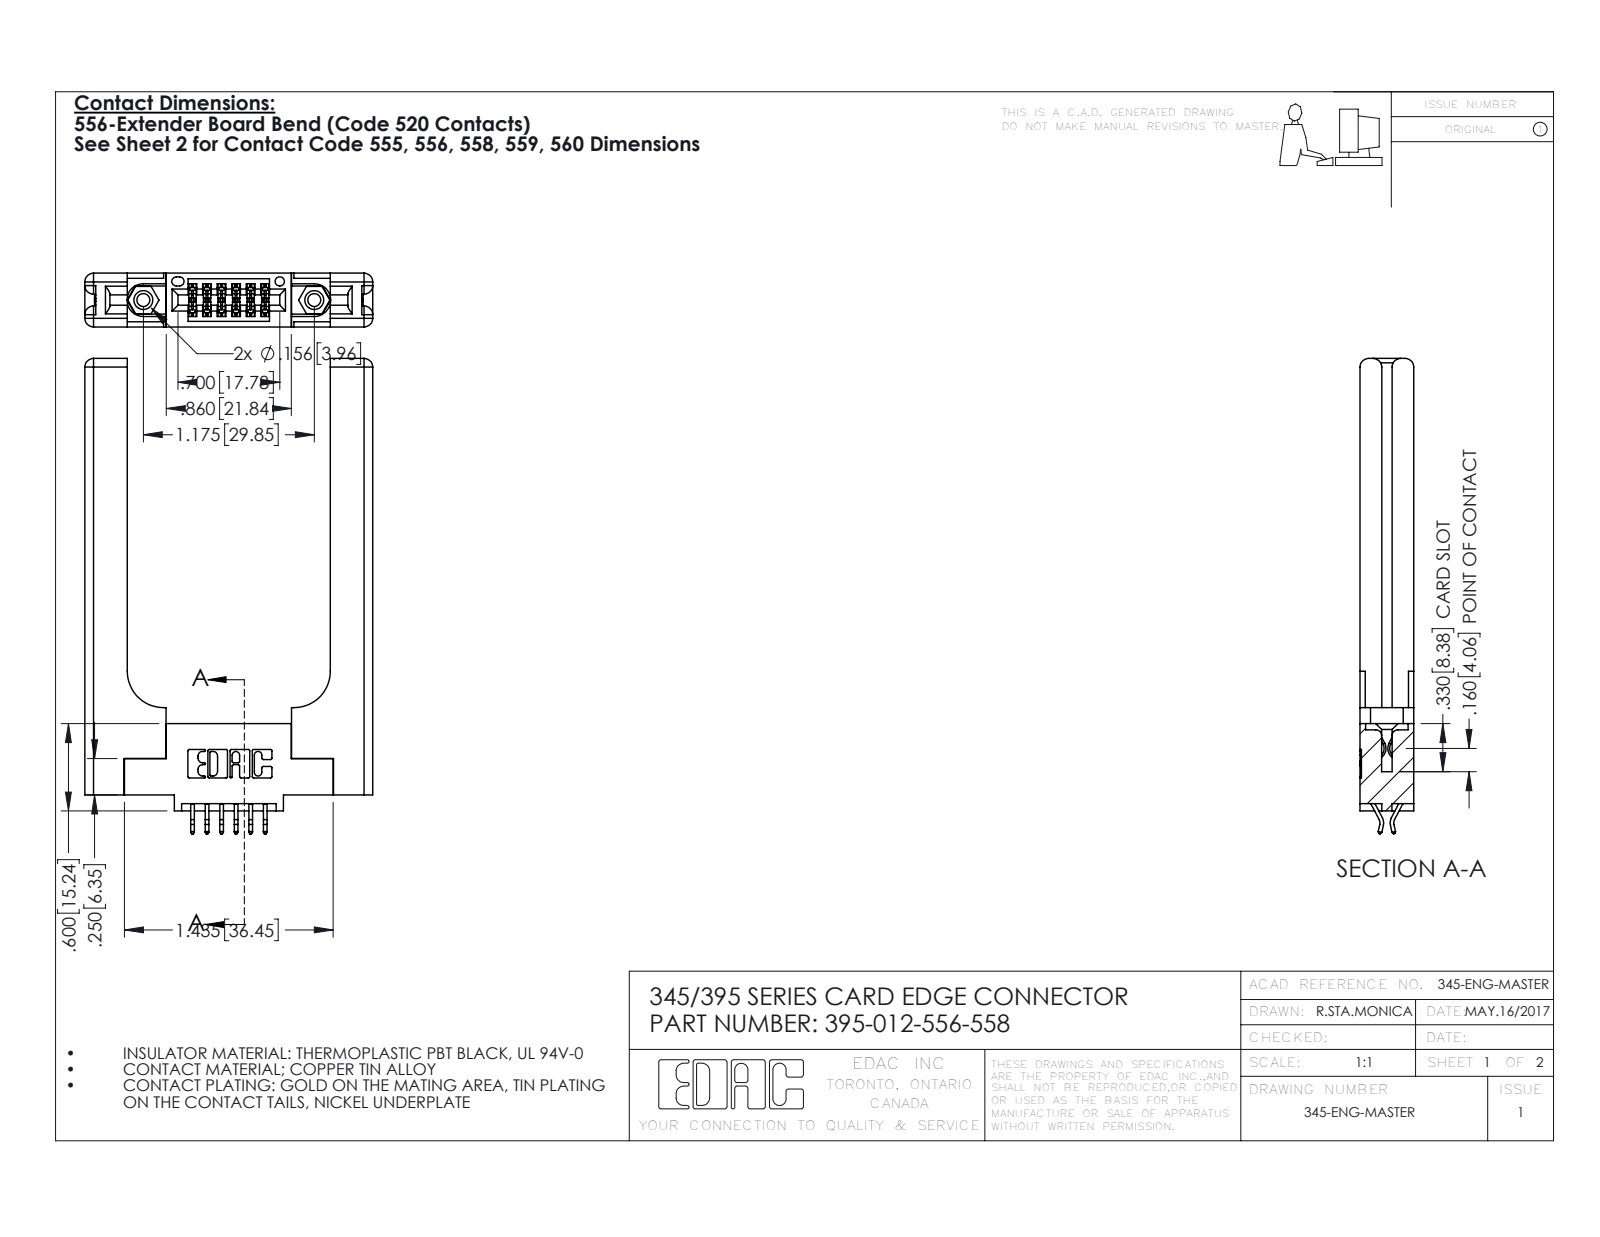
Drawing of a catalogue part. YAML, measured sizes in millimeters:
part_name: "345 Part_0.110 Offset - 0.156 Dia-TH; 345-250-001_345-250-001-102; 345-220-058_345-220-058; 395-012-556-558 (+1 more)"
step_written_by: "SolidWorks 2016 (CONFIG_CONTROL_DESIGN)"
units: millimeters
bodies: {solids: 17, faces: 1058, planar: 676, cylindrical: 322, other: 60}
overall_size: [83, 50.3, 9.4]
volume: 12900
surface_area: 11060
round_holes:
  - {diameter: 2.3, count: 2}
  - {diameter: 3.2, count: 2}
  - {diameter: 4, count: 2}
  - {diameter: 1.6, count: 1}
round_bosses_or_shafts:
  - {diameter: 3.9, count: 2}
partial_cylinders:
  - {radius: 0.3, count: 22}
  - {radius: 0.2, count: 18}
  - {radius: 1.5, count: 16}
  - {radius: 0.2, count: 6}
  - {radius: 0.8, count: 6}
  - {radius: 0.7, count: 3}
  - {radius: 0.3, count: 2}
  - {radius: 0.4, count: 2}
face_to_face_distances: [9.4, 3.8, 5.6, 1.8, 3.8, 2, 35.5, 7.6, 1.8, 7.4]
hole_center_spacings: [6.9, 24, 29.8]
